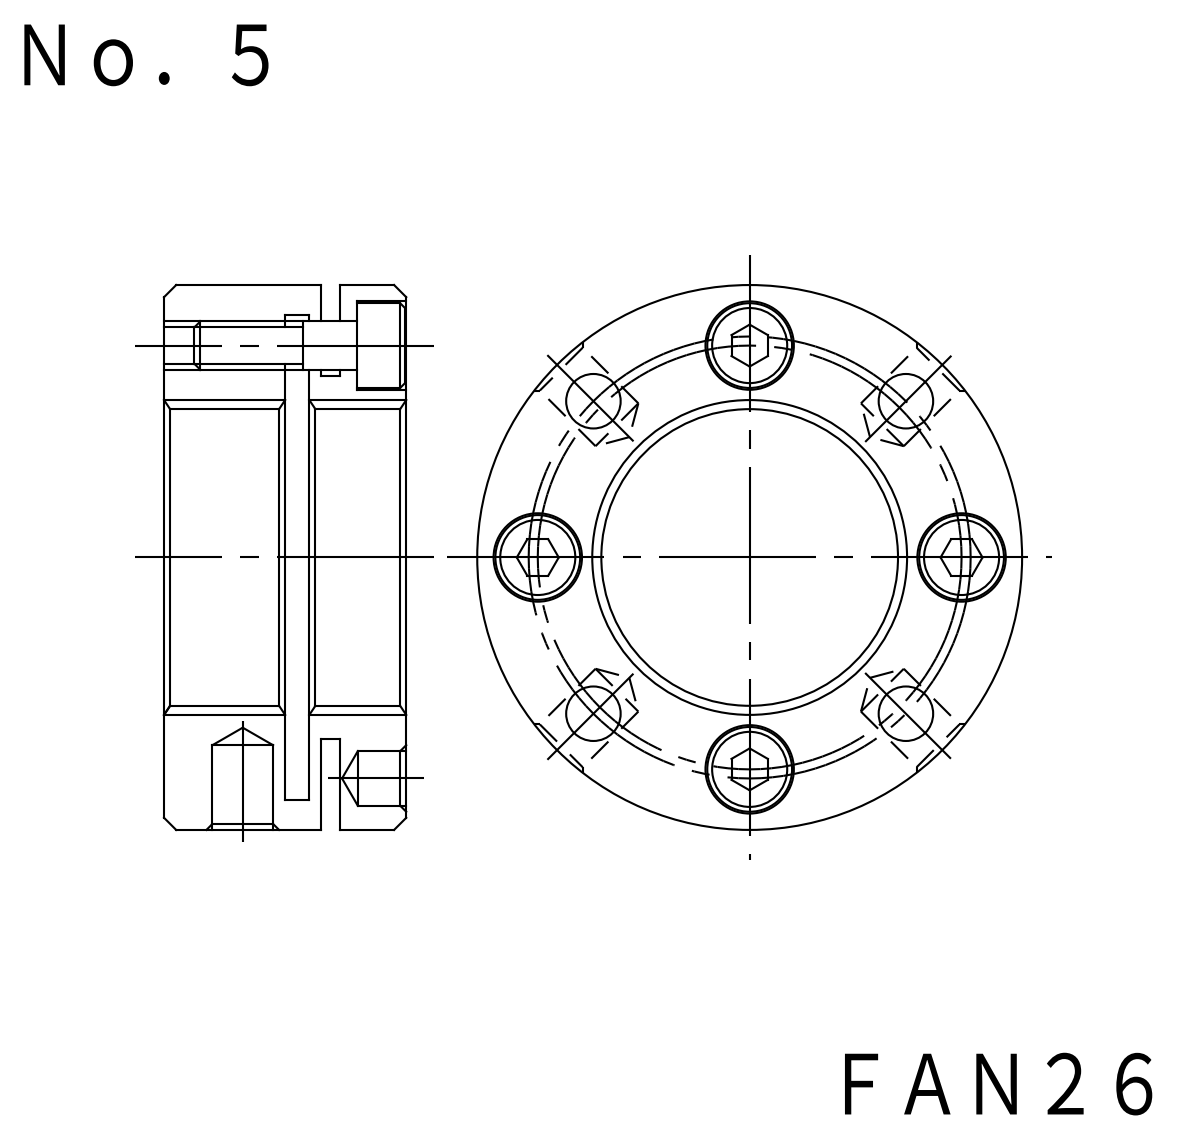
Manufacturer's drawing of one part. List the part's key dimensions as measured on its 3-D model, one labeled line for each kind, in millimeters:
Part name (STEP PRODUCT): FKD FAN26; M4X14_default
STEP written by: SolidWorks 2012 (CONFIG_CONTROL_DESIGN)
Units: millimetres
Bodies: 5 solids, 142 faces (50 planar, 76 cylindrical, 16 other)
Overall size (bounding box): 45 × 45 × 20
Volume: 17 305 mm³ · Surface area: 12 432 mm²
Round holes (diameter × count): ⌀3.24 ×4, ⌀4.3 ×4, ⌀4.5 ×4, ⌀7.3 ×4, ⌀5 ×2, ⌀26 ×1, ⌀40 ×1
Round bosses / shafts (diameter × count): ⌀7 ×4, ⌀4 ×4, ⌀45 ×1, ⌀30 ×1
Main face-to-face distances: 2, 3, 20, 12.3, 7.7, 14.3, 5.7, 9.3, 5, 10.7
Hole centre spacings: 13.7, 33.02, 17.5, 18.24, 24.75, 25.8, 35, 36.49
